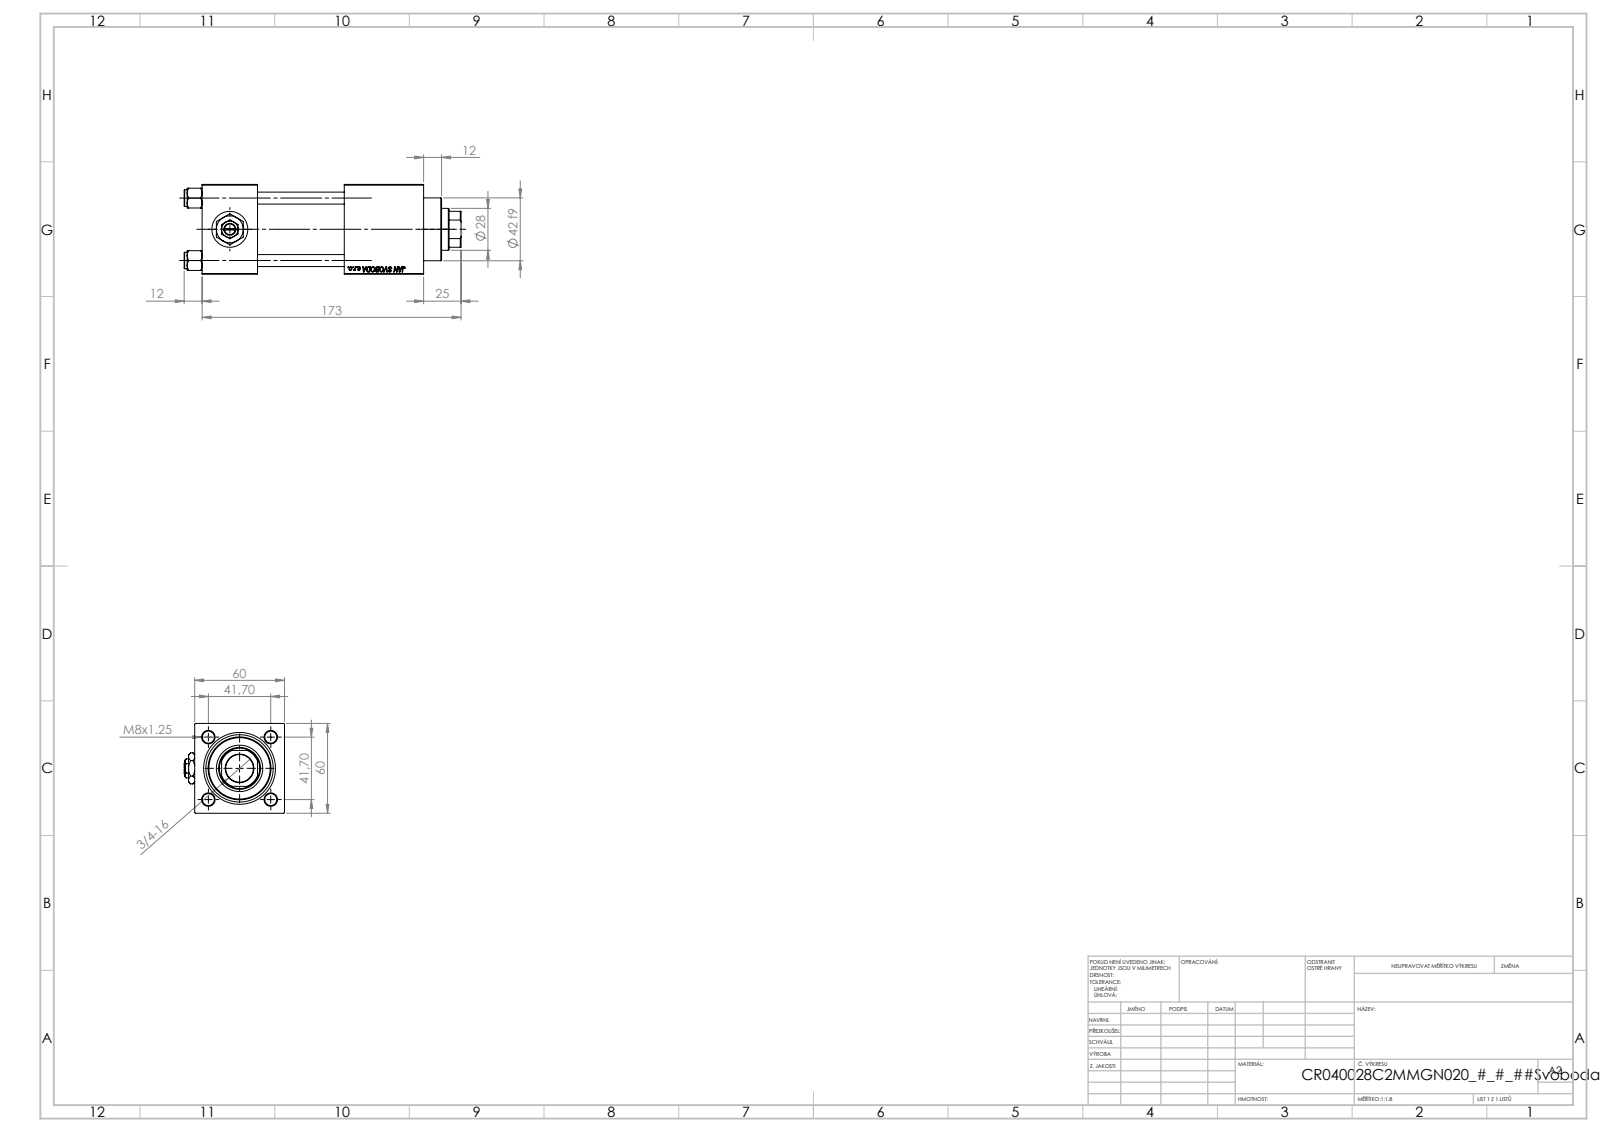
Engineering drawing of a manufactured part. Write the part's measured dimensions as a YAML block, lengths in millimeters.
part_name: "V215CR_C_Body; NUT_M5_C; V215_VC_A; V215CR_VCP_C (+2 more)"
step_written_by: "SolidWorks 2019 (CONFIG_CONTROL_DESIGN)"
units: millimeters
bodies: {solids: 12, faces: 1202, planar: 550, cylindrical: 94, other: 558}
overall_size: [185, 67, 60]
volume: 422827
surface_area: 113084
round_holes:
  - {diameter: 8, count: 4}
  - {diameter: 7, count: 2}
  - {diameter: 16.66, count: 2}
  - {diameter: 24, count: 2}
  - {diameter: 18.5, count: 1}
  - {diameter: 28, count: 1}
  - {diameter: 31, count: 1}
  - {diameter: 40, count: 1}
  - {diameter: 45, count: 1}
round_bosses_or_shafts:
  - {diameter: 11, count: 4}
  - {diameter: 46, count: 1}
  - {diameter: 42, count: 1}
partial_cylinders:
  - {radius: 13.5, count: 1}
face_to_face_distances: [60, 37, 58, 95, 53, 119.3, 82.3, 24.3, 148, 111]
hole_center_spacings: [29.49, 41.7, 58.97, 92.5]
